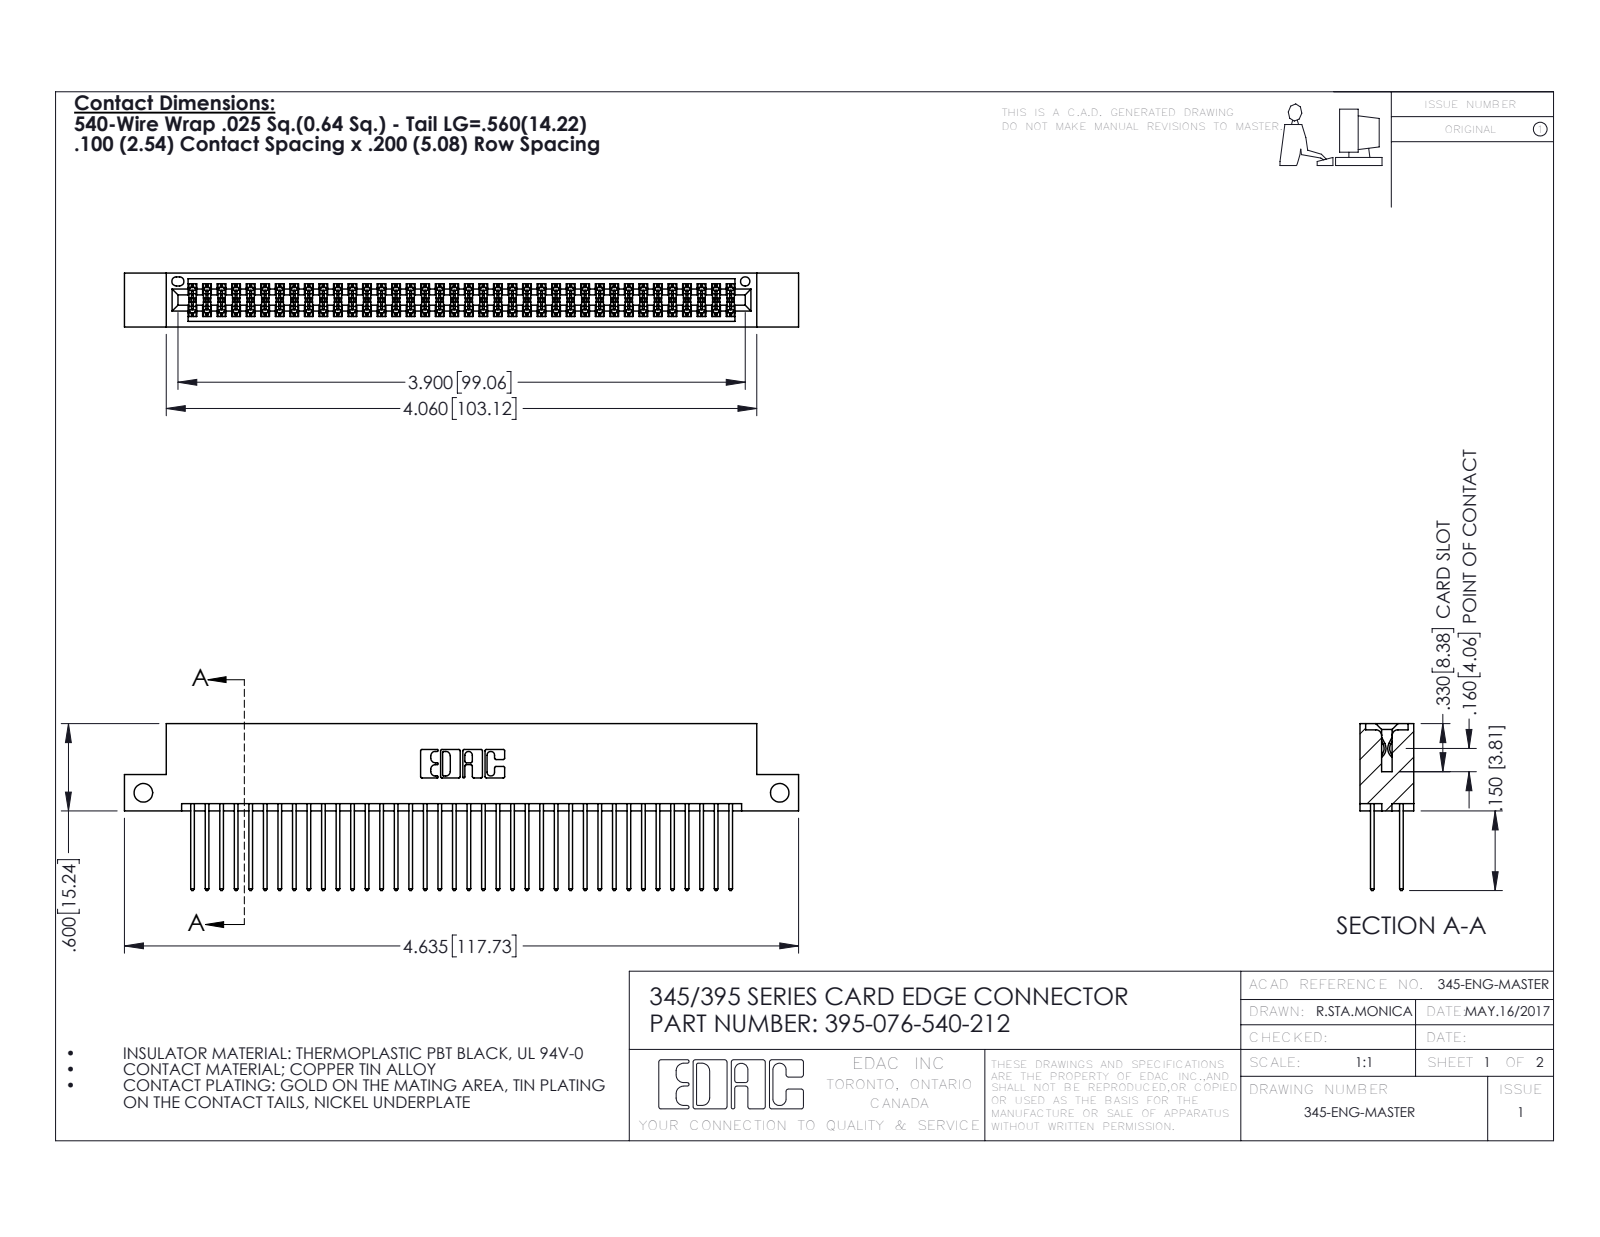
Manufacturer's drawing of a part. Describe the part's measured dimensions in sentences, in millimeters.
The part is named "345-292-001_345-293-140; 345 Part_Flush Mounting Lugs - Side Mount; 395-076-540-212". Its 3-D file was written by "SolidWorks 2016 (CONFIG_CONTROL_DESIGN)". It is 77 solids with 3926 faces: 2588 planar, 1338 cylindrical and 0 other. Overall it measures 117.7 by 29.1 by 9.4 millimeters. Its volume is 11 600 cubic millimeters and its surface area 18 270 square millimeters. Round holes: 2 of diameter 3.3, 1 of diameter 1.6. Partial cylindrical surfaces (rounded edges, fillets, slot ends): 114 of radius 0.2, 76 of radius 0.3, 22 of radius 0.3, 6 of radius 0.2, 6 of radius 0.8, 3 of radius 0.7, 2 of radius 0.4, 2 of radius 0.5. The main face-to-face distances are 7.6, 1.8, 5.1, 2.5, 6.9, 0.6, 9.4, 5.7, 4.4, 3.8. The hole center spacings are 111.1.
